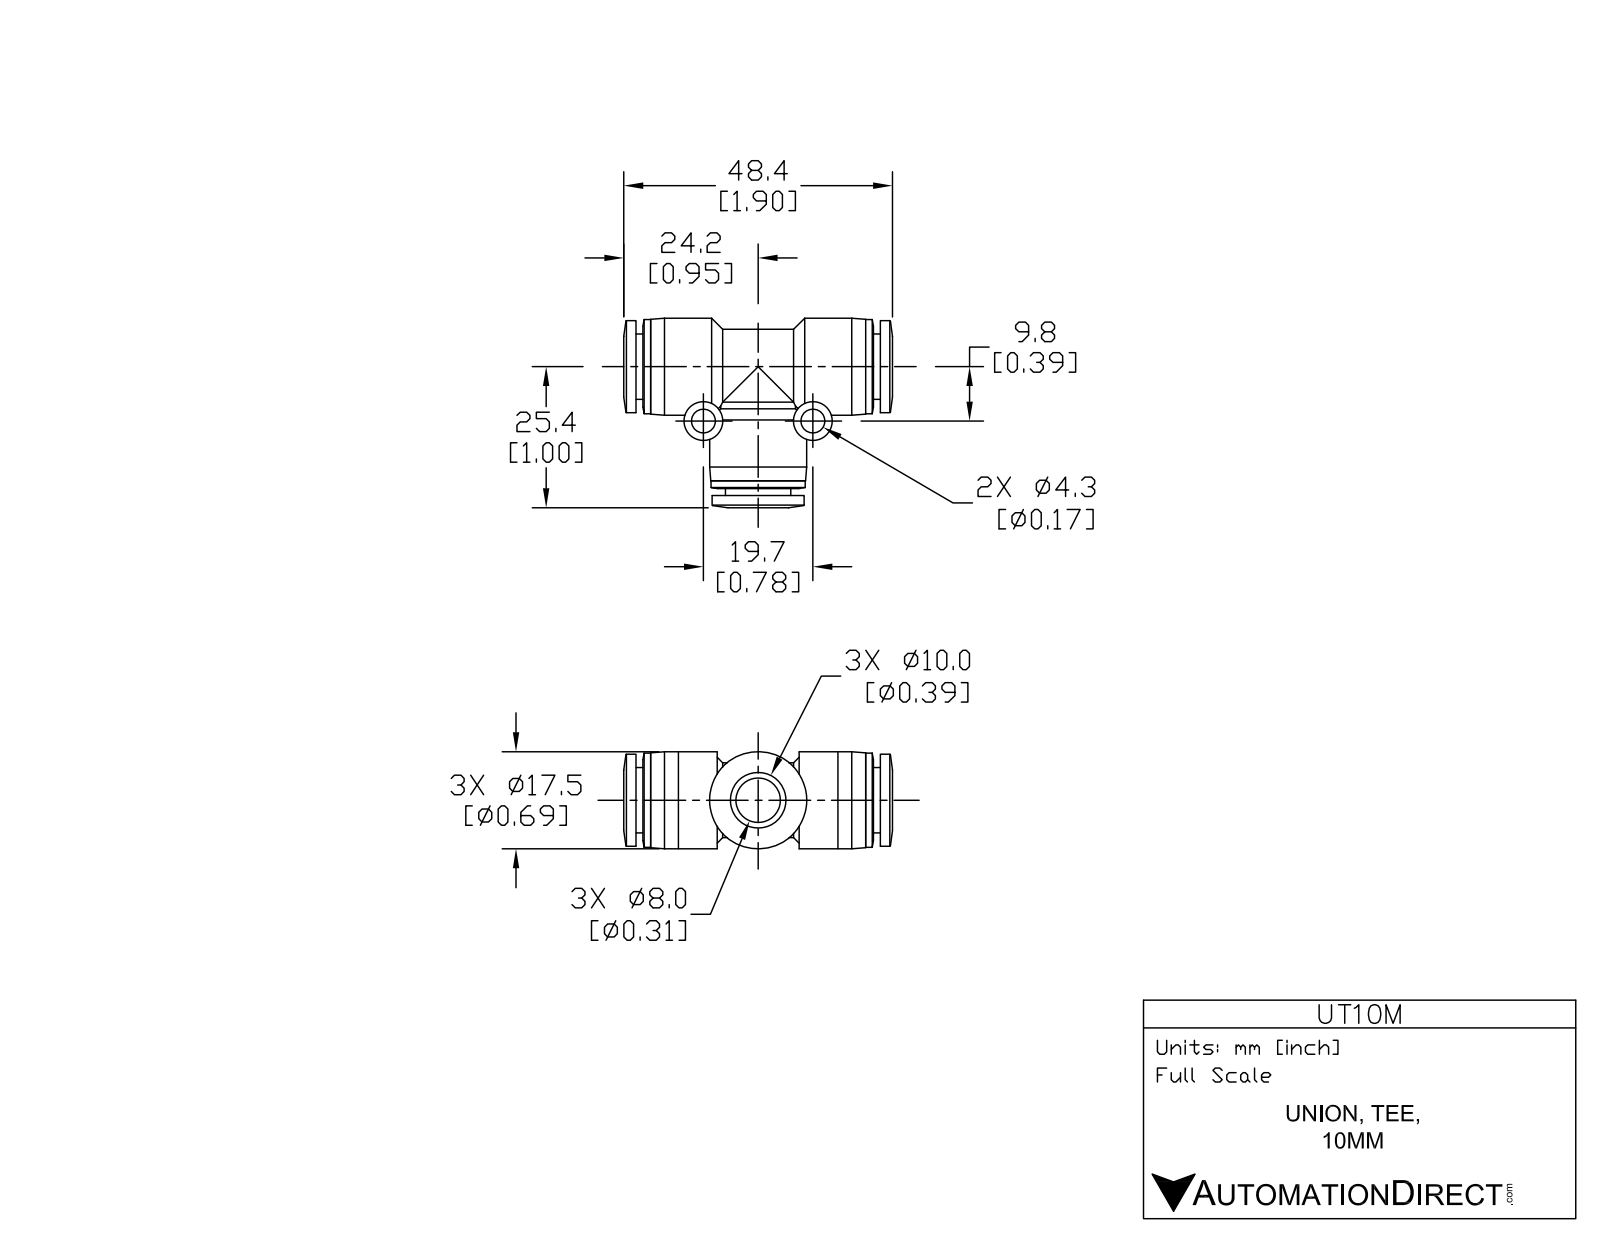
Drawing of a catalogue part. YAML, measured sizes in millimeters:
part_name: "UT10M"
step_written_by: "SolidWorks 2015 (AUTOMOTIVE_DESIGN)"
units: millimeters
bodies: {solids: 1, faces: 98, planar: 19, cylindrical: 49, other: 30}
overall_size: [48.5, 34.2, 17.5]
volume: 9090
surface_area: 7652
round_holes:
  - {diameter: 4.3, count: 2}
  - {diameter: 8, count: 2}
  - {diameter: 10.3, count: 2}
round_bosses_or_shafts:
  - {diameter: 17.5, count: 2}
  - {diameter: 17, count: 2}
  - {diameter: 16.6, count: 2}
  - {diameter: 13.5, count: 2}
  - {diameter: 11.8, count: 2}
  - {diameter: 7, count: 2}
face_to_face_distances: [1.2, 17.5, 42.8, 44.1, 16.3, 26.6, 25.3, 41.6, 9.1, 2.6]
hole_center_spacings: [21.8]
